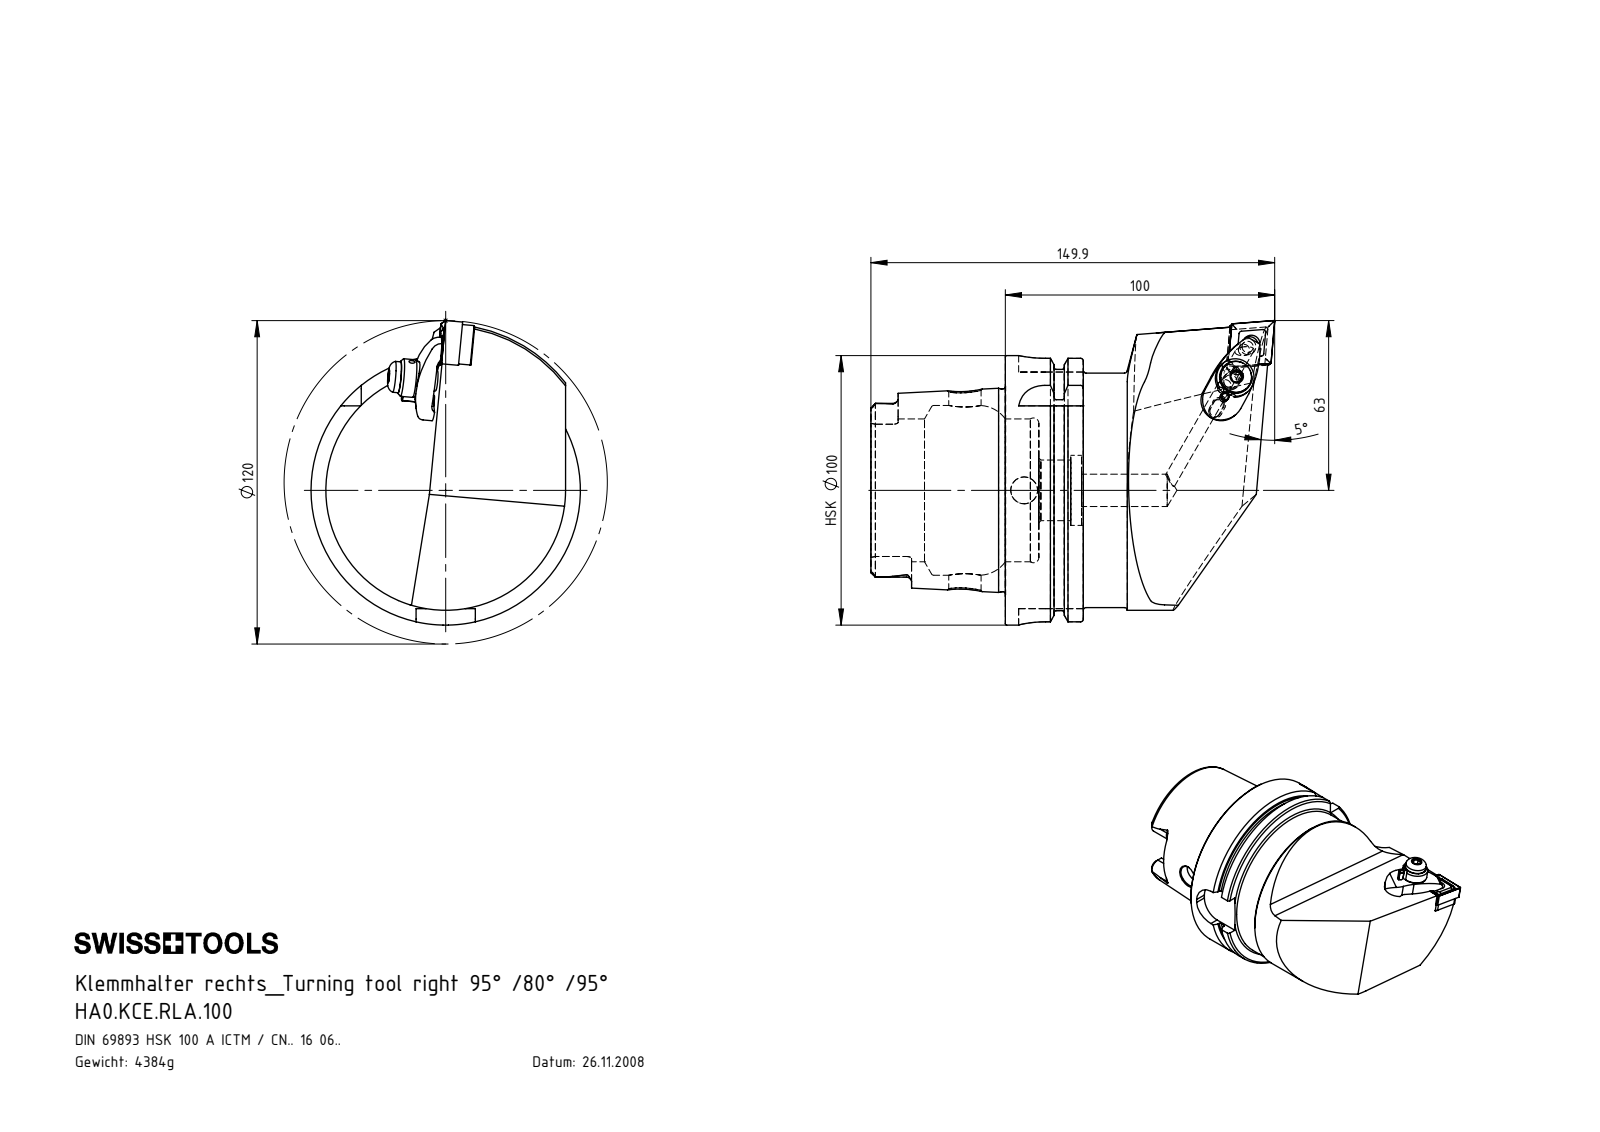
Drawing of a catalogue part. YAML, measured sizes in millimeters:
part_name: "WCC-ER3.102.024_C; CNMG160604; WCC-ER5.102.012_B; WCE-ER2.001.012_A (+7 more)"
step_written_by: "SolidWorks 2017 (AUTOMOTIVE_DESIGN)"
units: millimeters
bodies: {solids: 11, faces: 464, planar: 120, cylindrical: 154, other: 190}
overall_size: [149.9, 113, 100]
volume: 557326
surface_area: 75203
round_holes:
  - {diameter: 2, count: 3}
  - {diameter: 4.2, count: 2}
  - {diameter: 5, count: 2}
  - {diameter: 7, count: 2}
  - {diameter: 12, count: 2}
  - {diameter: 2.4, count: 1}
  - {diameter: 3, count: 1}
  - {diameter: 4, count: 1}
  - {diameter: 6, count: 1}
  - {diameter: 6.2, count: 1}
  - {diameter: 6.35, count: 1}
  - {diameter: 7.9, count: 1}
round_bosses_or_shafts:
  - {diameter: 5, count: 2}
  - {diameter: 3, count: 2}
  - {diameter: 100, count: 1}
  - {diameter: 91.95, count: 1}
  - {diameter: 87, count: 1}
  - {diameter: 75.26, count: 1}
  - {diameter: 14, count: 1}
  - {diameter: 11.5, count: 1}
partial_cylinders:
  - {radius: 0.45, count: 6}
  - {radius: 1.9, count: 6}
  - {radius: 0.4, count: 4}
  - {radius: 0.79, count: 4}
  - {radius: 1, count: 4}
  - {radius: 10, count: 4}
  - {radius: 1.5, count: 3}
  - {radius: 0.79, count: 2}
face_to_face_distances: [12.45, 28.95, 16.5, 49.9, 62.35, 78.85, 87.8, 78.2, 28.3, 15.85]
hole_center_spacings: [15.4, 8, 10.6, 15.21, 23.4, 23.41, 5.97, 6.14]
